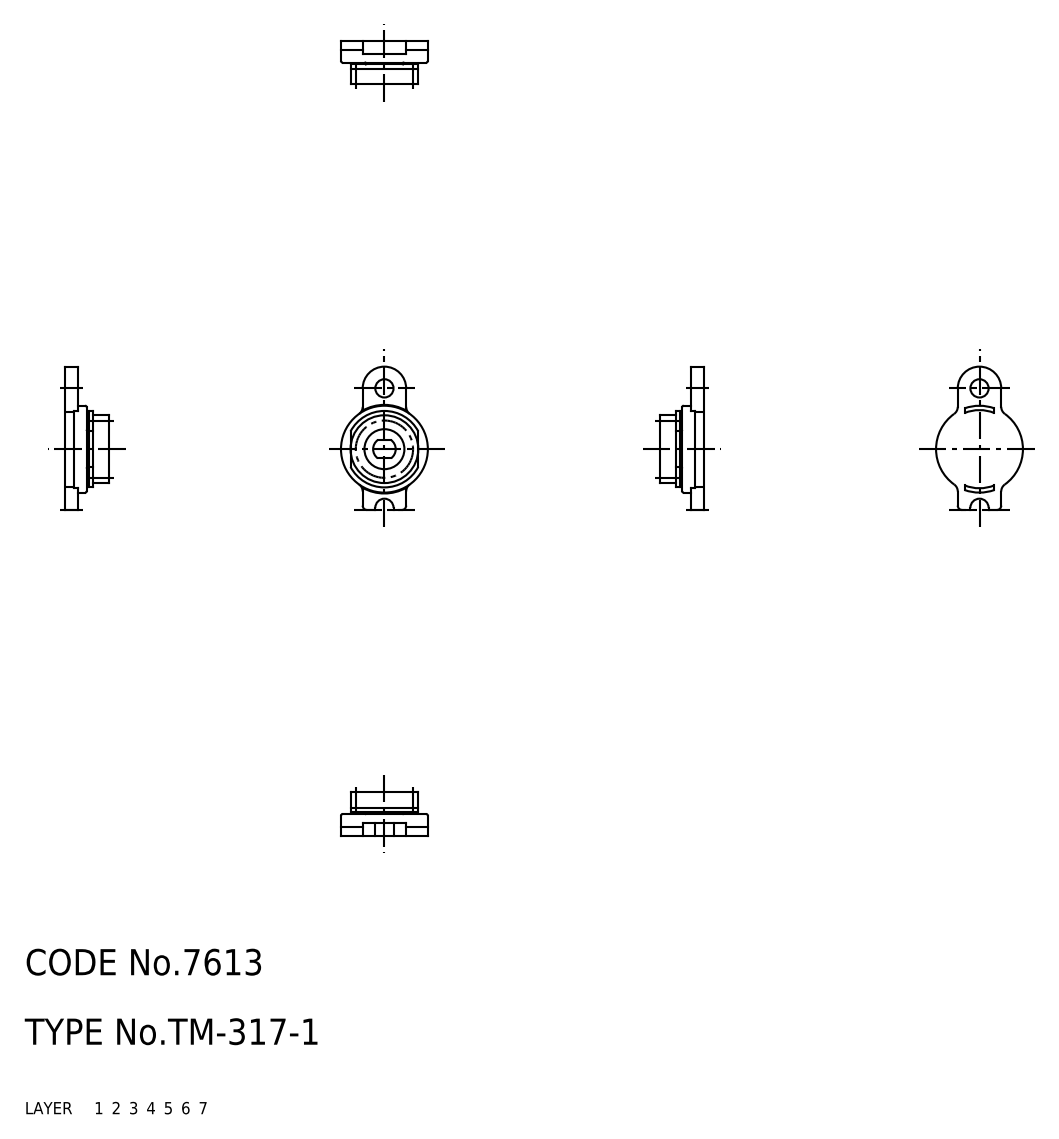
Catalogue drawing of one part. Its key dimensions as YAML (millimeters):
part_name: "67114316; 67114329"
step_written_by: "CADfix (AUTOMOTIVE_DESIGN)"
units: millimeters
bodies: {solids: 2, faces: 107, planar: 0, cylindrical: 0, other: 107}
overall_size: [16.5, 10, 5]
volume: 325
surface_area: 605
